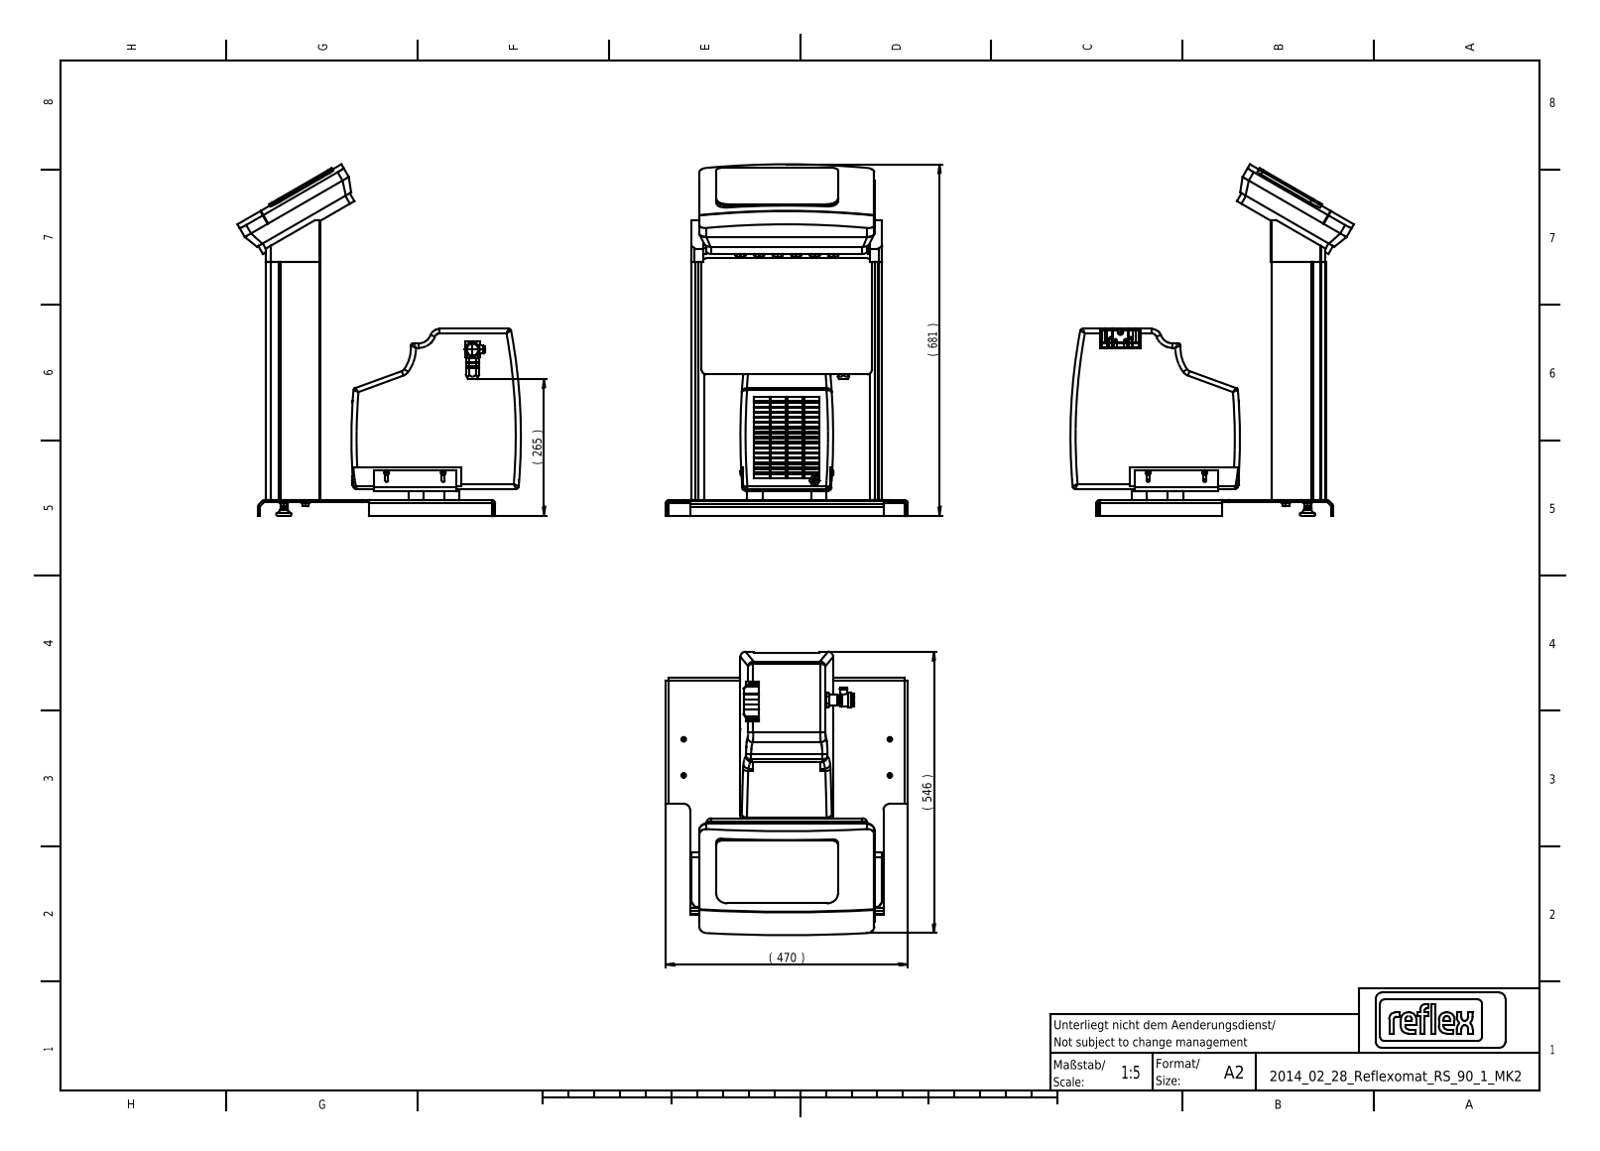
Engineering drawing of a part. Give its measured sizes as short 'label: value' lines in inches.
written by: Mechanical Desktop 2011 (CONFIG_CONTROL_DESIGN)
unit: in
bodies: 37 solids, 2133 faces (1430 planar, 360 cylindrical, 343 other)
size: 26.826 × 21.656 × 18.504
volume: 1 429 in³; area: 3 074 in²
holes: 20× ⌀0.354, 8× ⌀0.323, 8× ⌀0.413, 7× ⌀0.669, 4× ⌀0.331, 2× ⌀0.197, 2× ⌀0.906, 1× ⌀0.244, 1× ⌀0.256, 1× ⌀0.394, 1× ⌀0.551
bosses: 12× ⌀0.63, 8× ⌀0.315, 7× ⌀0.748, 7× ⌀0.689, 4× ⌀1.181, 3× ⌀0.394, 3× ⌀0.197, 2× ⌀0.827
rounds: 13× R0.394, 11× R0.197, 9× R0.098, 6× R0.256, 5× R0.118, 4× R0.354, 4× R0.551, 2× R0.02
face distances: 0.157, 0.866, 0.945, 0.079, 1.024, 2.933, 0.709, 0.787, 12.283, 13.228
hole spacings: 4.921, 2.756, 5.641, 5.443, 5.6, 5.83, 1.417, 0.75
